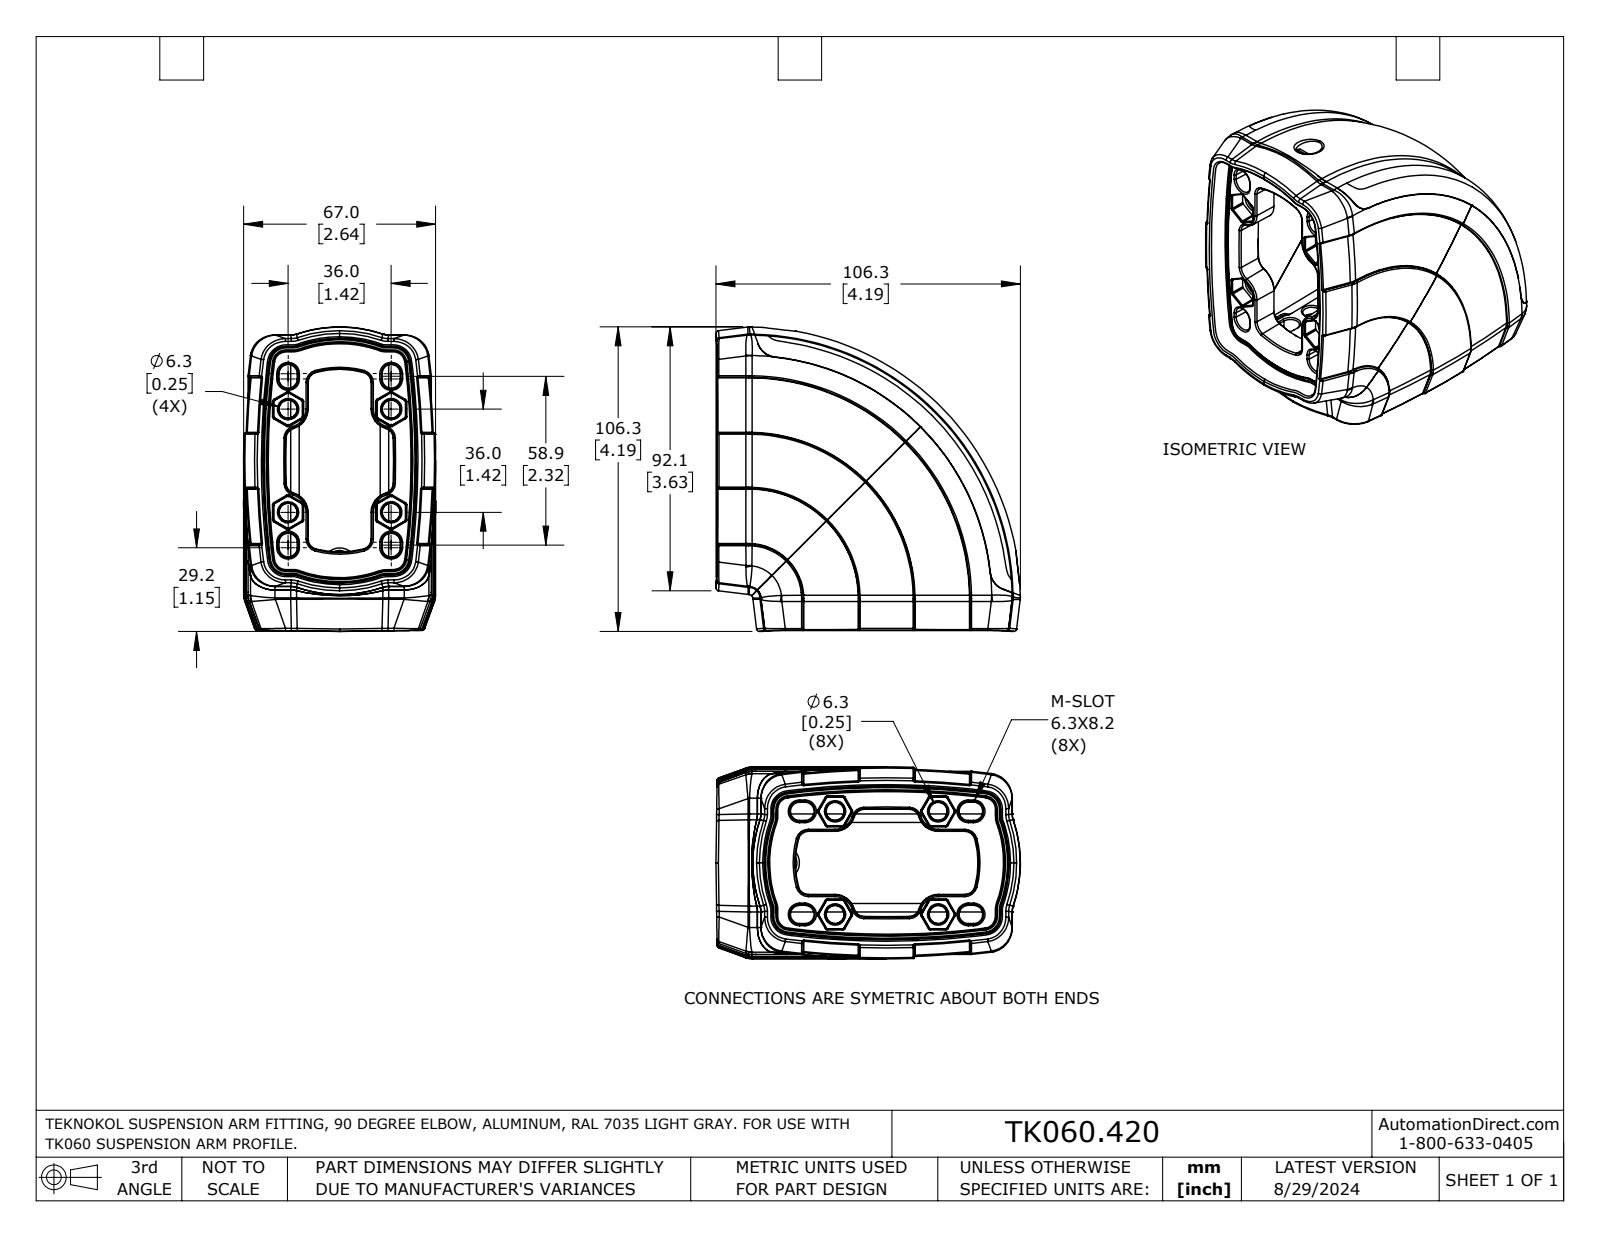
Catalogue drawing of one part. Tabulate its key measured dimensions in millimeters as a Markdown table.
| quantity | value |
| --- | --- |
| part name | TK060.420 |
| STEP written by | SolidWorks 2023 (AUTOMOTIVE_DESIGN) |
| units | millimeters |
| bodies | 1 solid, 1303 faces (138 planar, 208 cylindrical, 957 other) |
| overall size | 106.3 × 106.3 × 67 |
| volume | 215 700 mm³ |
| surface area | 70 650 mm² |
| partial cylindrical surfaces (radius × count) | 0.5 × 56, 0.4 × 40, 0.2 × 12, 2.4 × 12, 1 × 8, 0.5 × 6, 2.1 × 4, 6.4 × 4 |
| main face-to-face distances | 9.2, 0.5, 8.7, 18, 5.3, 4, 31.2, 36, 13.2, 49.2 |
